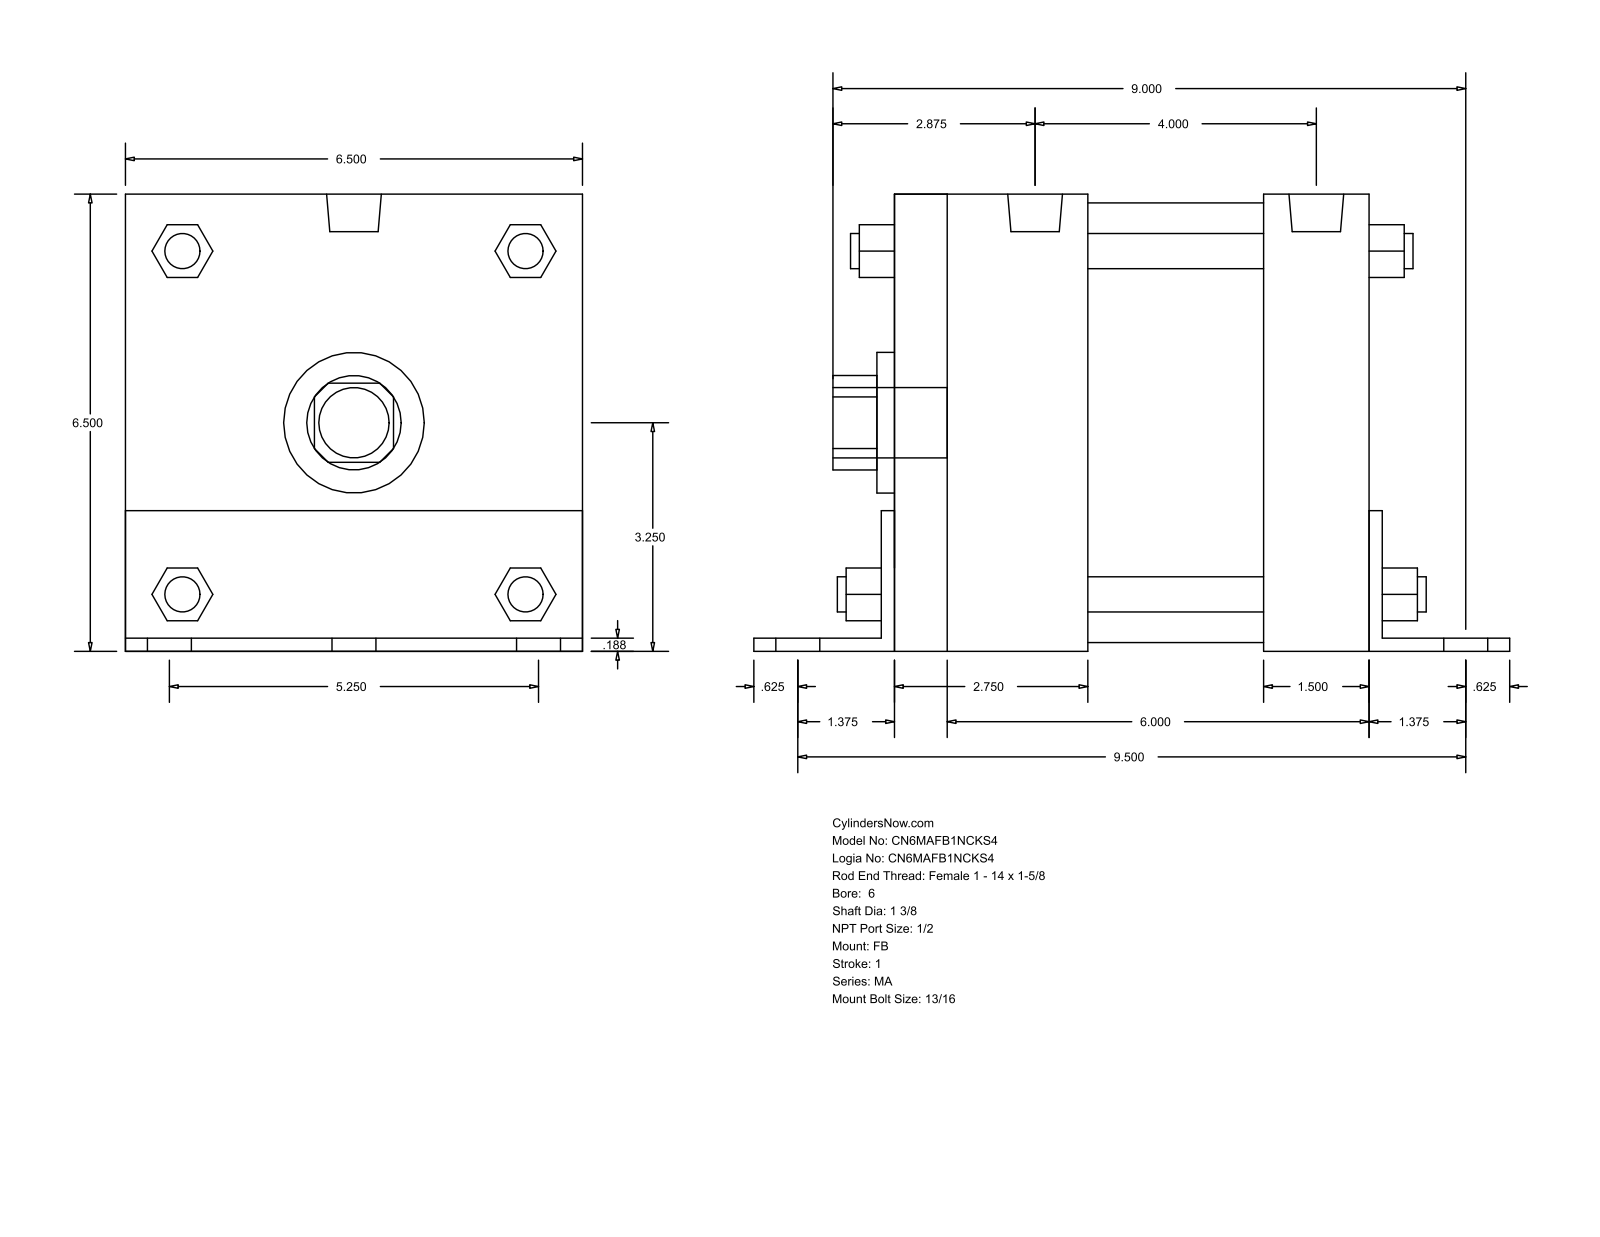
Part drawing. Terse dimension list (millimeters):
name: MA_FB__0600_1.375
written by: GSSL Pune (CONFIG_CONTROL_DESIGN)
unit: mm
bodies: 0 solids, 140 faces (105 planar, 35 cylindrical, 0 other)
size: 269.88 × 165.15 × 165.1
holes: 1× ⌀34.92, 1× ⌀50.8, 1× ⌀158.75
bosses: 6× ⌀20.64, 4× ⌀17.46, 4× ⌀12.7, 2× ⌀19.77, 1× ⌀25.4
rounds: 1× R17.06, 1× R32.05
face distances: 165.1, 4.76, 168.27, 165.15, 4.71, 160.39, 4.77, 38.1, 173.04, 177.8
